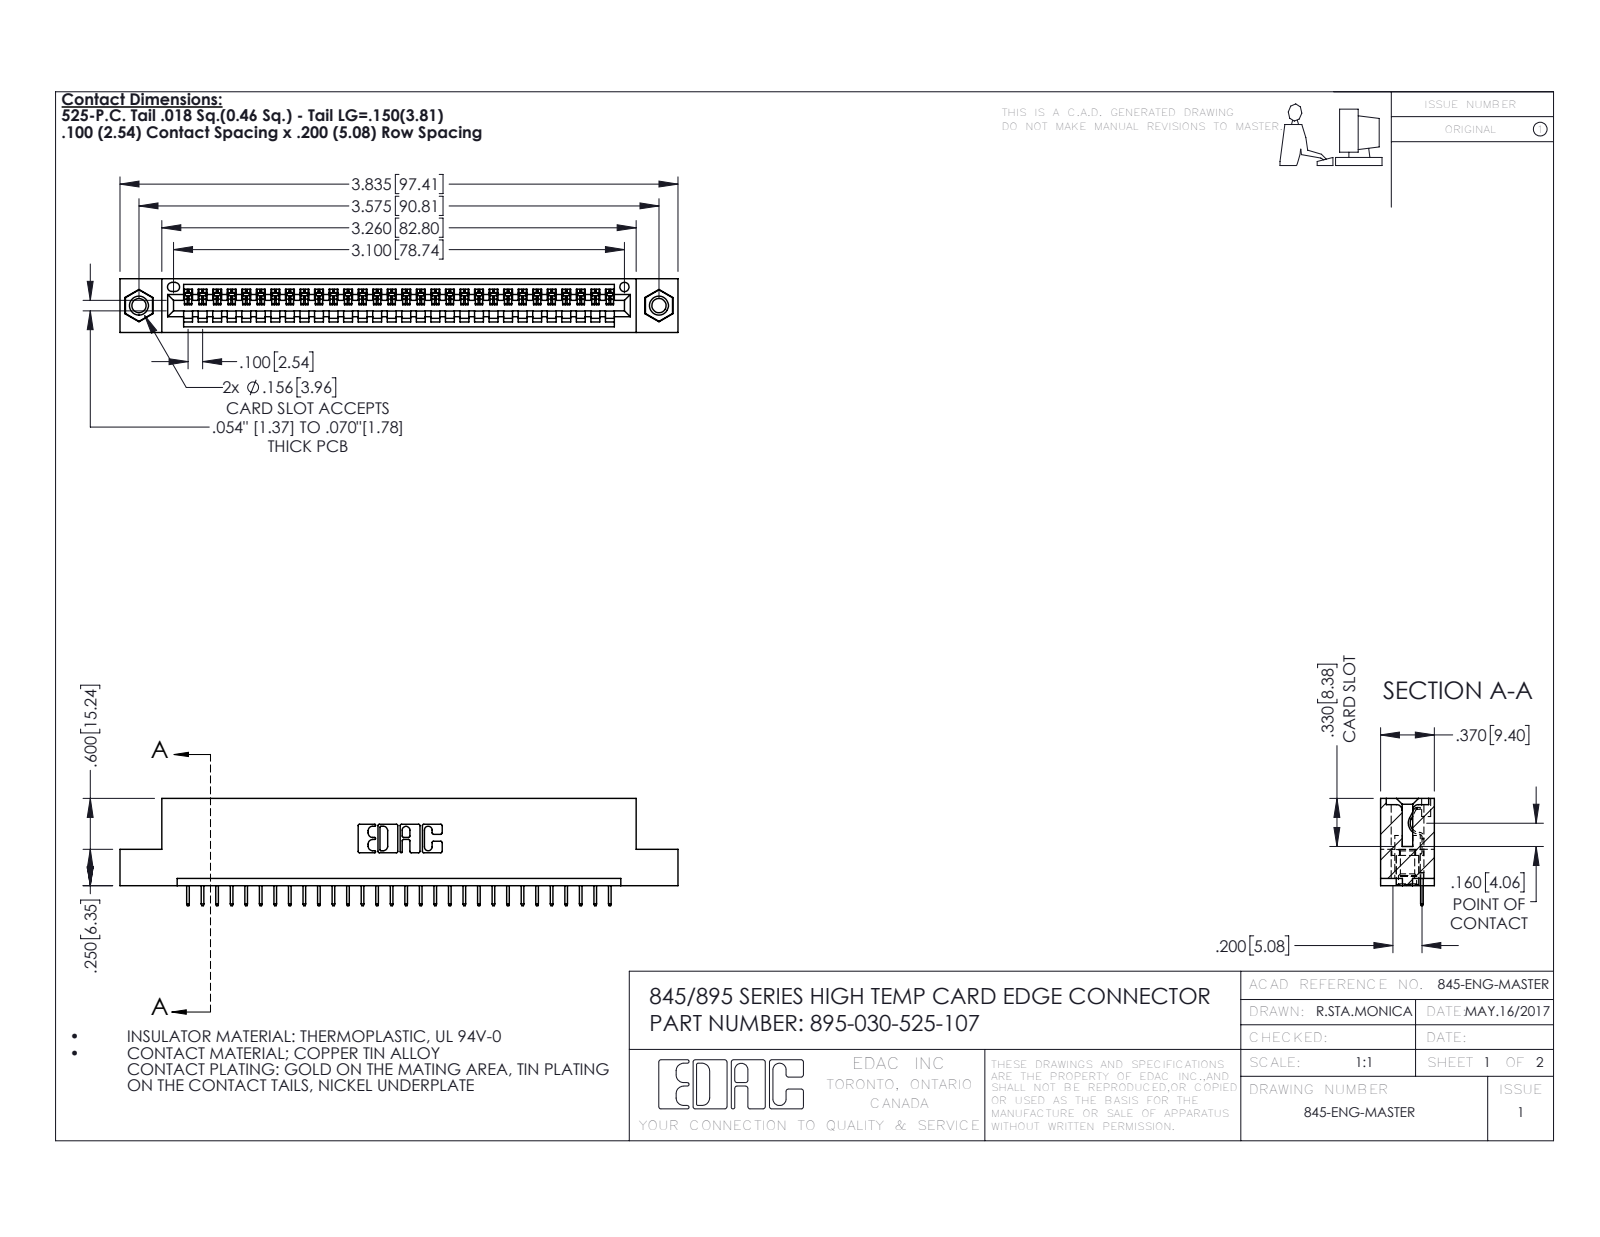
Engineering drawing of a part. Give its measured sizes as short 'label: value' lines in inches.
name: 845 Part_Flush Mounting Lugs - 0.156 Dia-TI; 895-030-525-107; 345-250-001_345-250-005-103; 345-292-001_345-293-125
written by: SolidWorks 2020 (CONFIG_CONTROL_DESIGN)
unit: in
bodies: 33 solids, 2046 faces (1492 planar, 538 cylindrical, 16 other)
size: 3.835 × 0.737 × 0.37
volume: 0.55 in³; area: 17.74 in²
holes: 2× ⌀0.098, 2× ⌀0.125, 2× ⌀0.156, 1× ⌀0.064
bosses: 2× ⌀0.155
rounds: 60× R0.006, 22× R0.01, 6× R0.007, 6× R0.031, 3× R0.026, 2× R0.031, 2× R0.04, 1× R0.014
face distances: 0.072, 0.298, 0.37, 0.2, 0.098, 0.272, 0.025, 0.225, 0.072, 0.149
hole spacings: 0.27, 3.34, 3.575
